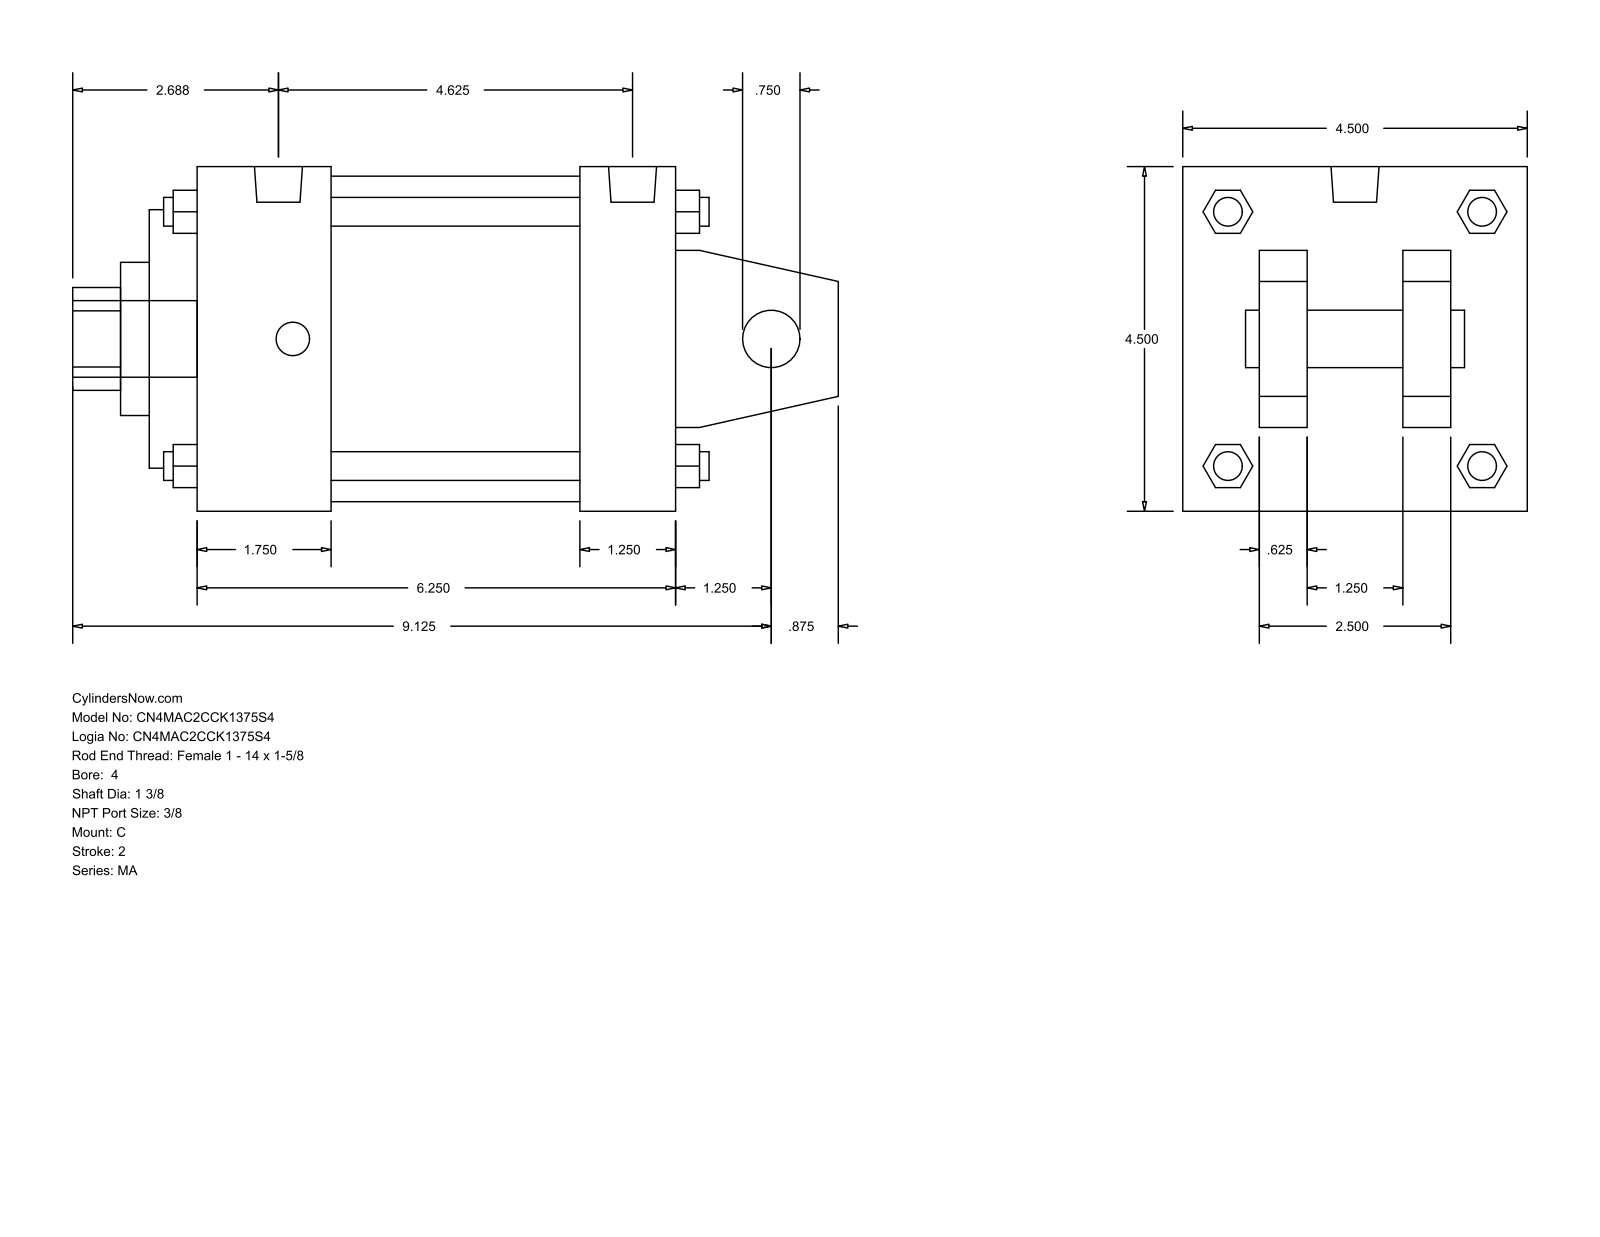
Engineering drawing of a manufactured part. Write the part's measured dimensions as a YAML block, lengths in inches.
part_name: "MA_C__0400_1.375"
step_written_by: "GSSL Pune (CONFIG_CONTROL_DESIGN)"
units: inches
bodies: {solids: 0, faces: 141, planar: 109, cylindrical: 32, other: 0}
overall_size: [10, 4.5, 4.5]
round_holes:
  - {diameter: 0.75, count: 1}
  - {diameter: 1.375, count: 1}
  - {diameter: 2, count: 1}
  - {diameter: 3.375, count: 1}
  - {diameter: 4.25, count: 1}
round_bosses_or_shafts:
  - {diameter: 0.437, count: 4}
  - {diameter: 0.375, count: 4}
  - {diameter: 0.627, count: 2}
  - {diameter: 1, count: 1}
partial_cylinders:
  - {radius: 0.672, count: 1}
face_to_face_distances: [4.5, 0.625, 6.25, 2.875, 1.625, 1, 3.5, 1.875, 6.875, 5.625]
